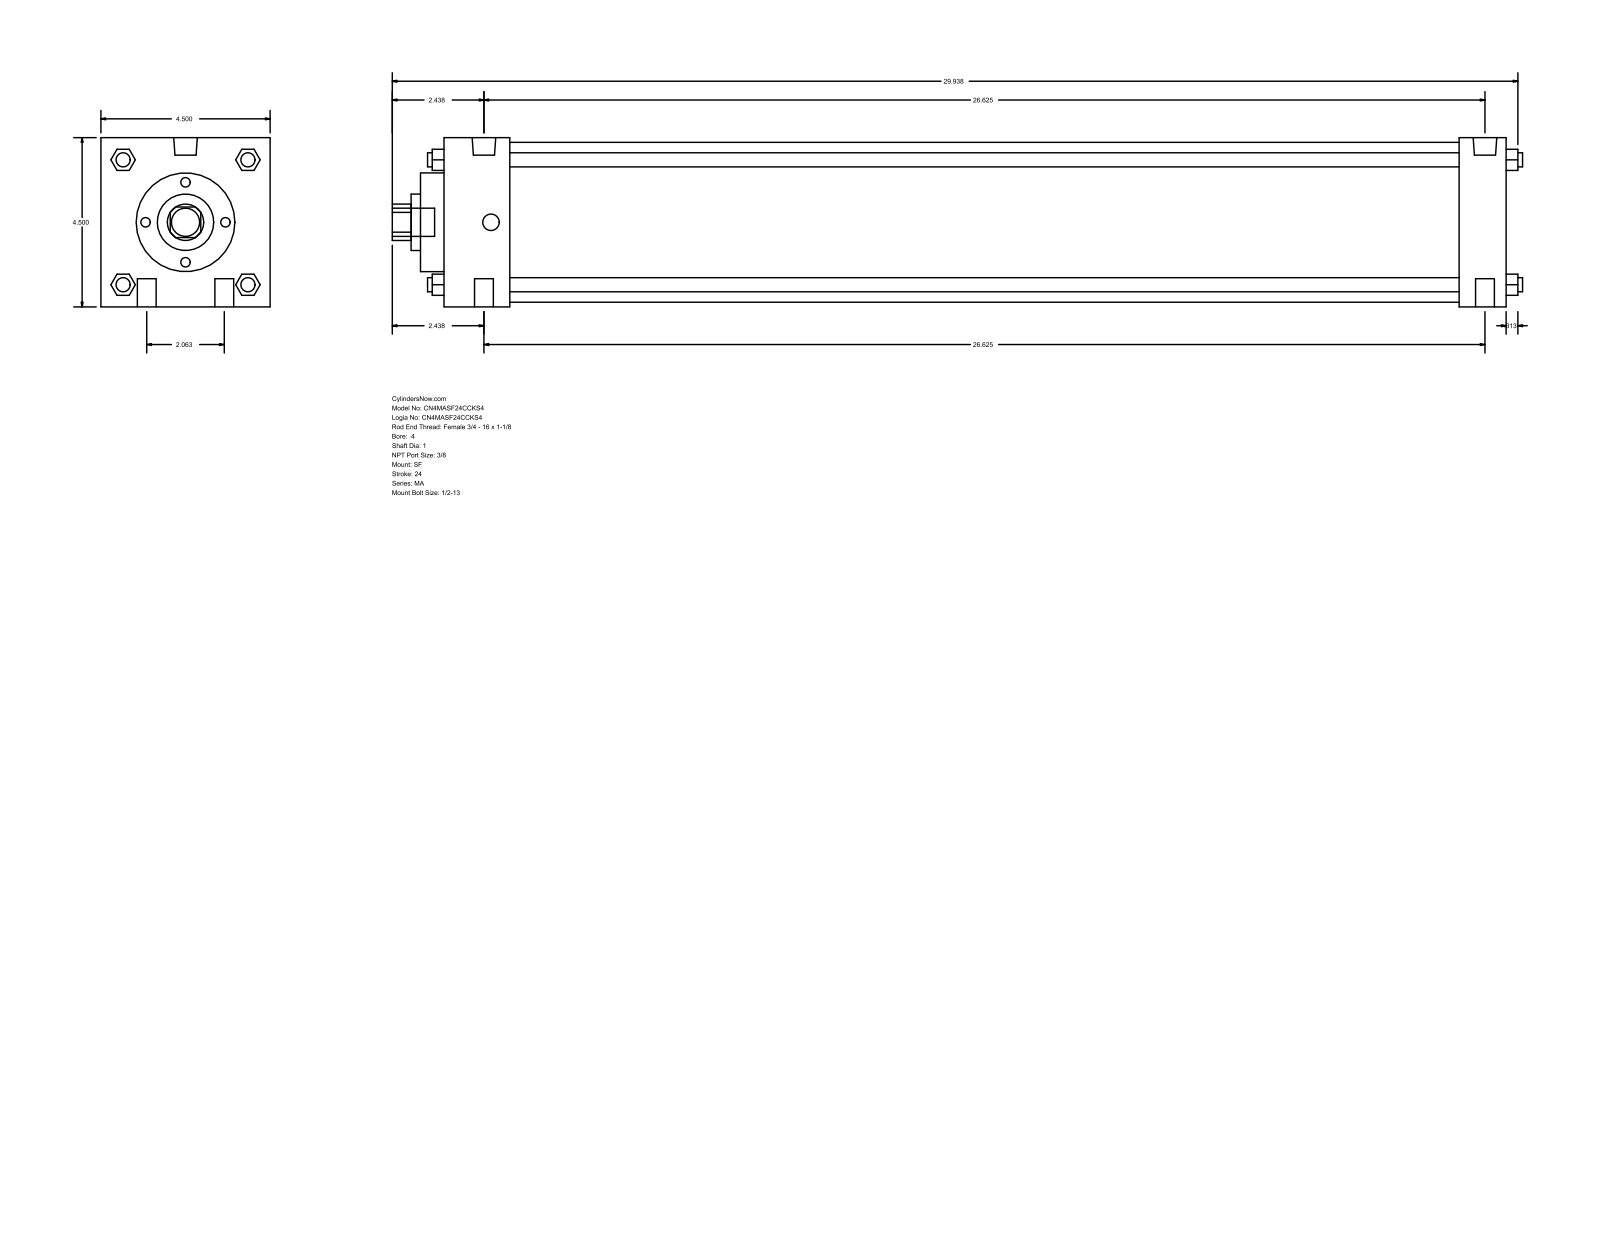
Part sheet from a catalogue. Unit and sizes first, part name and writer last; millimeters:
Units: millimetres
Overall size (bounding box): 763.59 × 114.3 × 114.3
Round holes (diameter × count): ⌀25.4 ×1, ⌀38.1 ×1, ⌀66.67 ×1, ⌀107.95 ×1
Round bosses / shafts (diameter × count): ⌀12.7 ×4, ⌀9.53 ×4, ⌀15.93 ×2, ⌀11.11 ×2, ⌀19.05 ×1
Partial cylindrical surfaces — rounded edges, fillets, slot ends (radius × count): R12.29 ×1
Main face-to-face distances: 114.3, 717.56, 685.81, 31.75, 44.46, 641.35, 673.1, 15.87, 60.33, 701.68
Bodies: 0 solids, 126 faces (95 planar, 31 cylindrical, 0 other)
Part name (STEP PRODUCT): MA_SF__0400_1
STEP written by: GSSL Pune (CONFIG_CONTROL_DESIGN)
